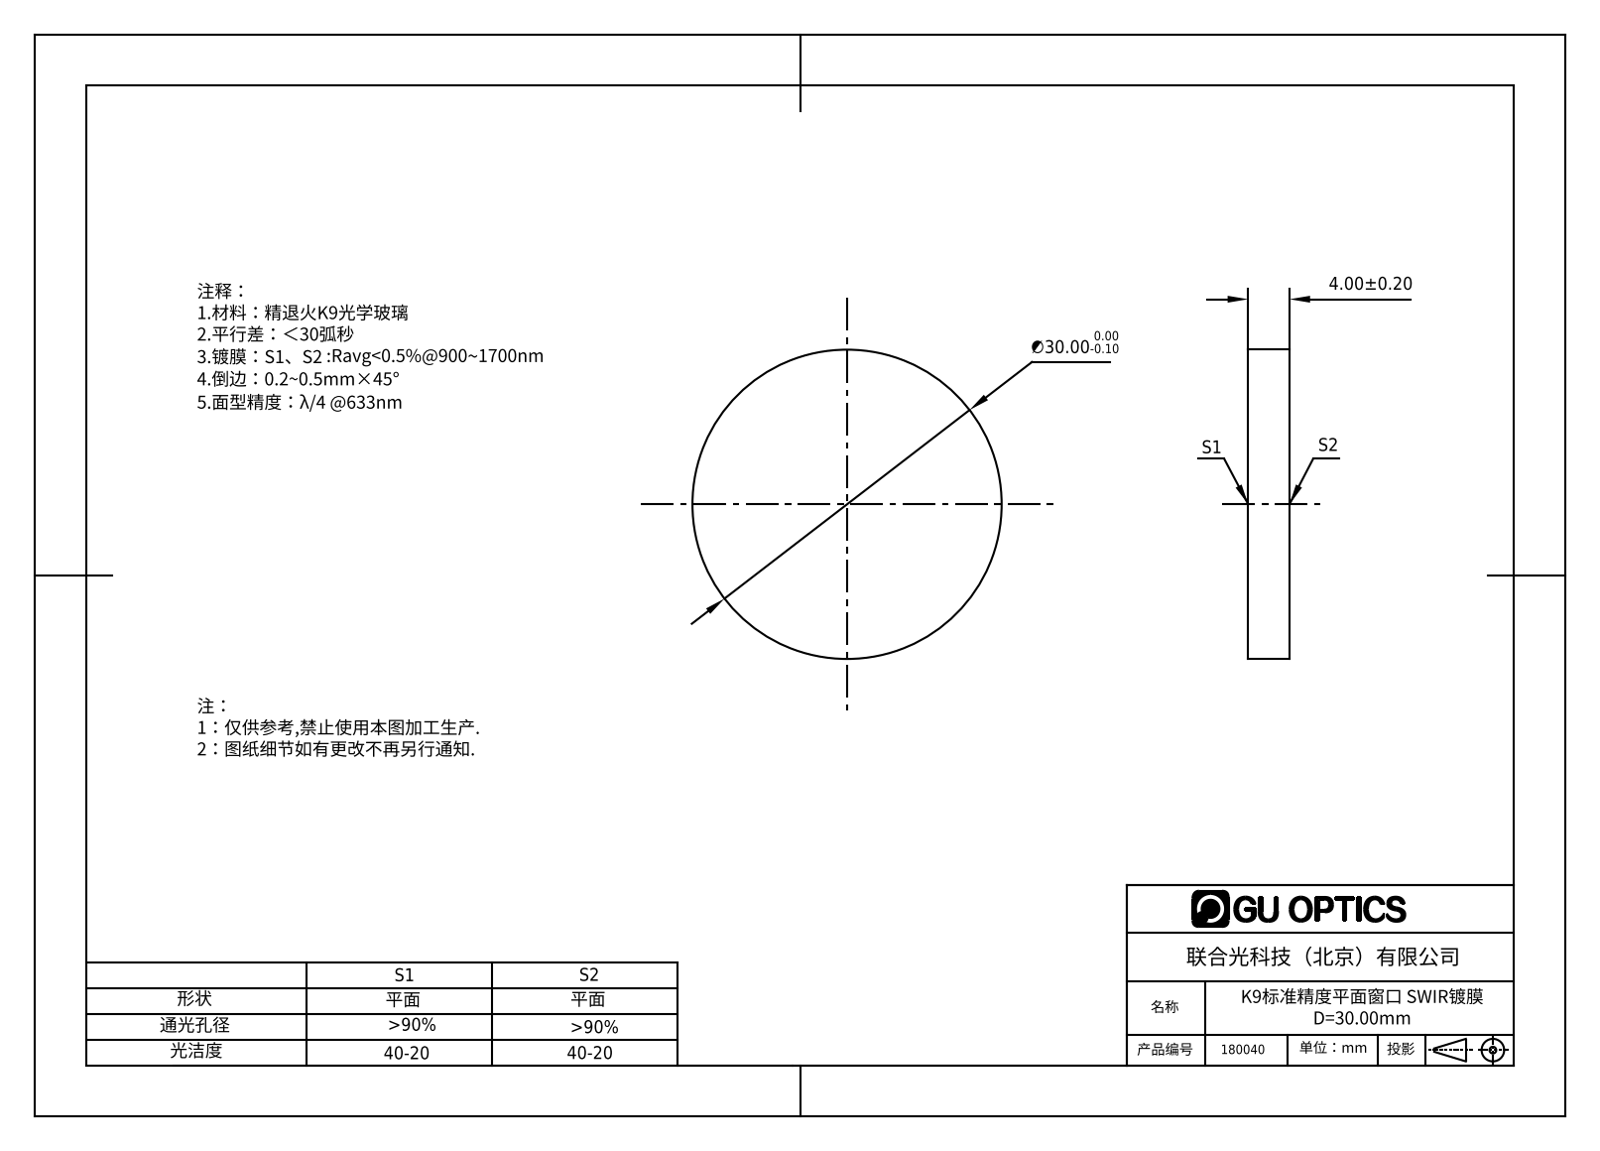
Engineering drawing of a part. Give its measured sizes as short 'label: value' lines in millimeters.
name: 180007
written by: SolidWorks 2016 (AUTOMOTIVE_DESIGN)
unit: mm
bodies: 1 solid, 4 faces (2 planar, 2 cylindrical, 0 other)
size: 30 × 30 × 4
volume: 2 827 mm³; area: 1 791 mm²
bosses: 1× ⌀30
face distances: 4
